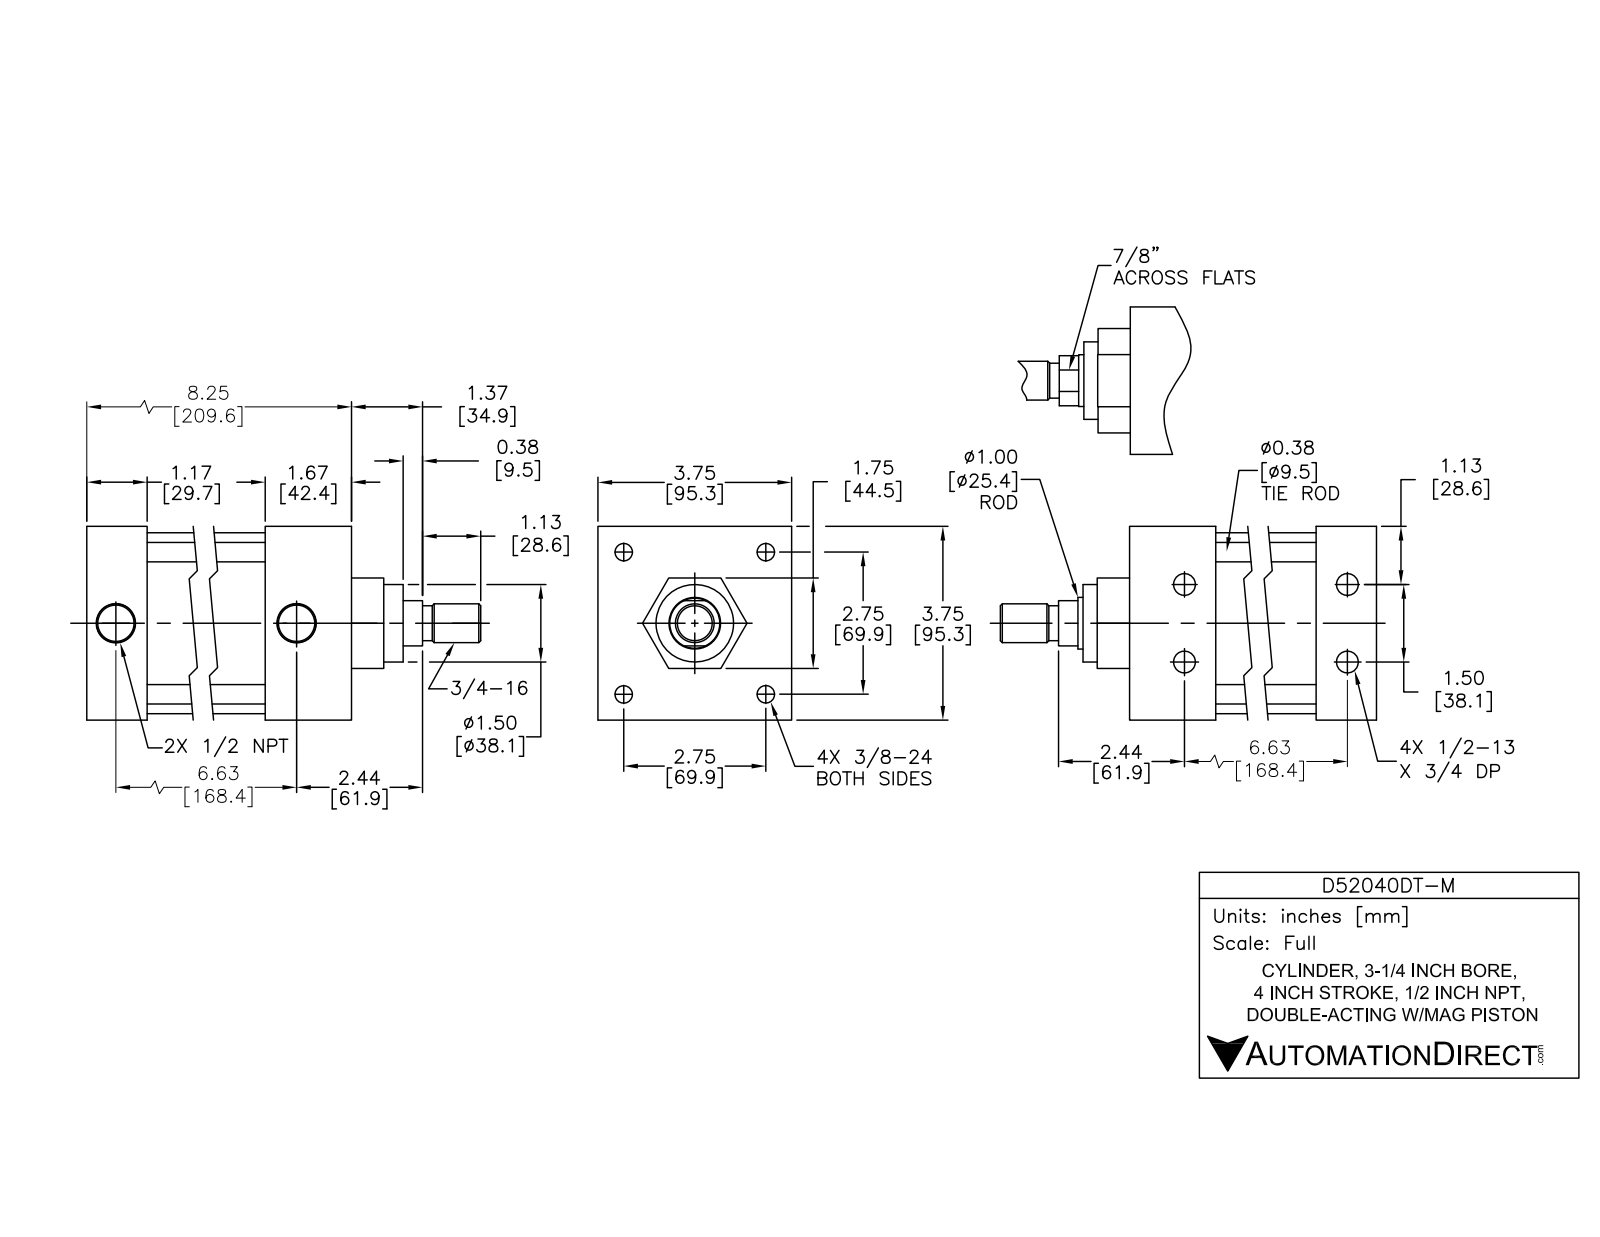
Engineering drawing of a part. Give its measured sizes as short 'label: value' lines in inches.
name: D52040DT-M BODY; D52040DT-M PISTON; D52040DT-M
written by: SolidWorks 2015 (AUTOMOTIVE_DESIGN)
unit: in
bodies: 12 solids, 303 faces (99 planar, 114 cylindrical, 90 other)
size: 10.745 × 3.75 × 3.75
volume: 63.7 in³; area: 351.5 in²
holes: 4× ⌀0.33, 4× ⌀0.406, 4× ⌀0.417, 4× ⌀0.625, 2× ⌀0.5, 2× ⌀0.766, 1× ⌀1, 1× ⌀1.003, 1× ⌀3.25
bosses: 4× ⌀0.609, 4× ⌀0.375, 4× ⌀0.34, 1× ⌀3.5, 1× ⌀3.247, 1× ⌀1.75, 1× ⌀0.997, 1× ⌀0.97
rounds: 4× R0.375
face distances: 3.75, 0.08, 5.326, 8.246, 1.75, 6.997, 1.249, 5.751, 1.246, 2.495
hole spacings: 2.758, 1.95, 0.75, 0.76, 1.5, 3.9, 6.5, 6.547
